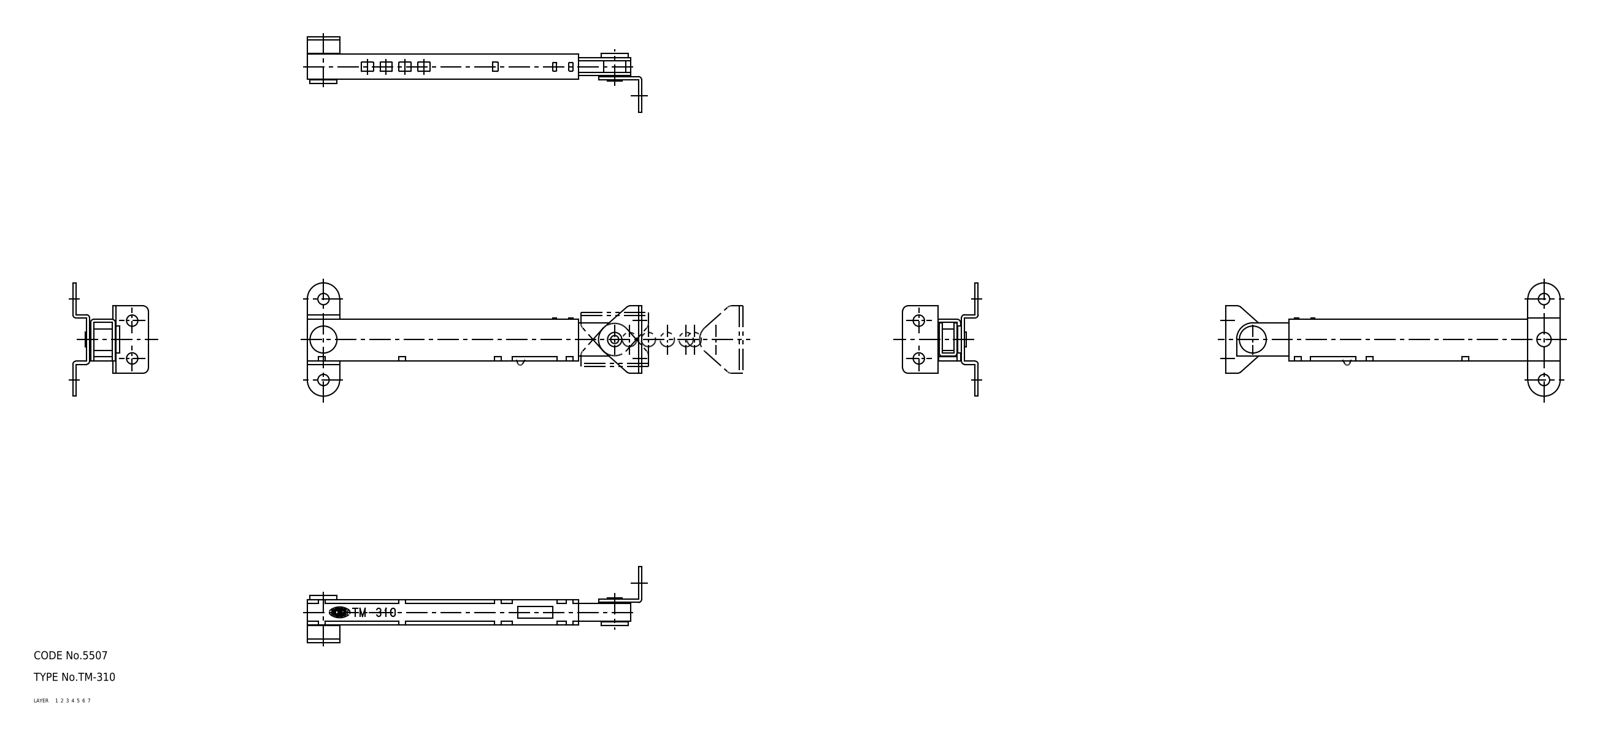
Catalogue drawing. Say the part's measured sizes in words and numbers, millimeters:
The part is named "67119801; 67119814; 67119827; 67119840 (+1 more)". Its 3-D file was written by "CADfix (AUTOMOTIVE_DESIGN)". It is 5 solids with 260 faces: 0 planar, 0 cylindrical and 260 other. Overall it measures 124 by 42 by 28 millimeters. Its volume is 11 492 cubic millimeters and its surface area 19 040 square millimeters.
